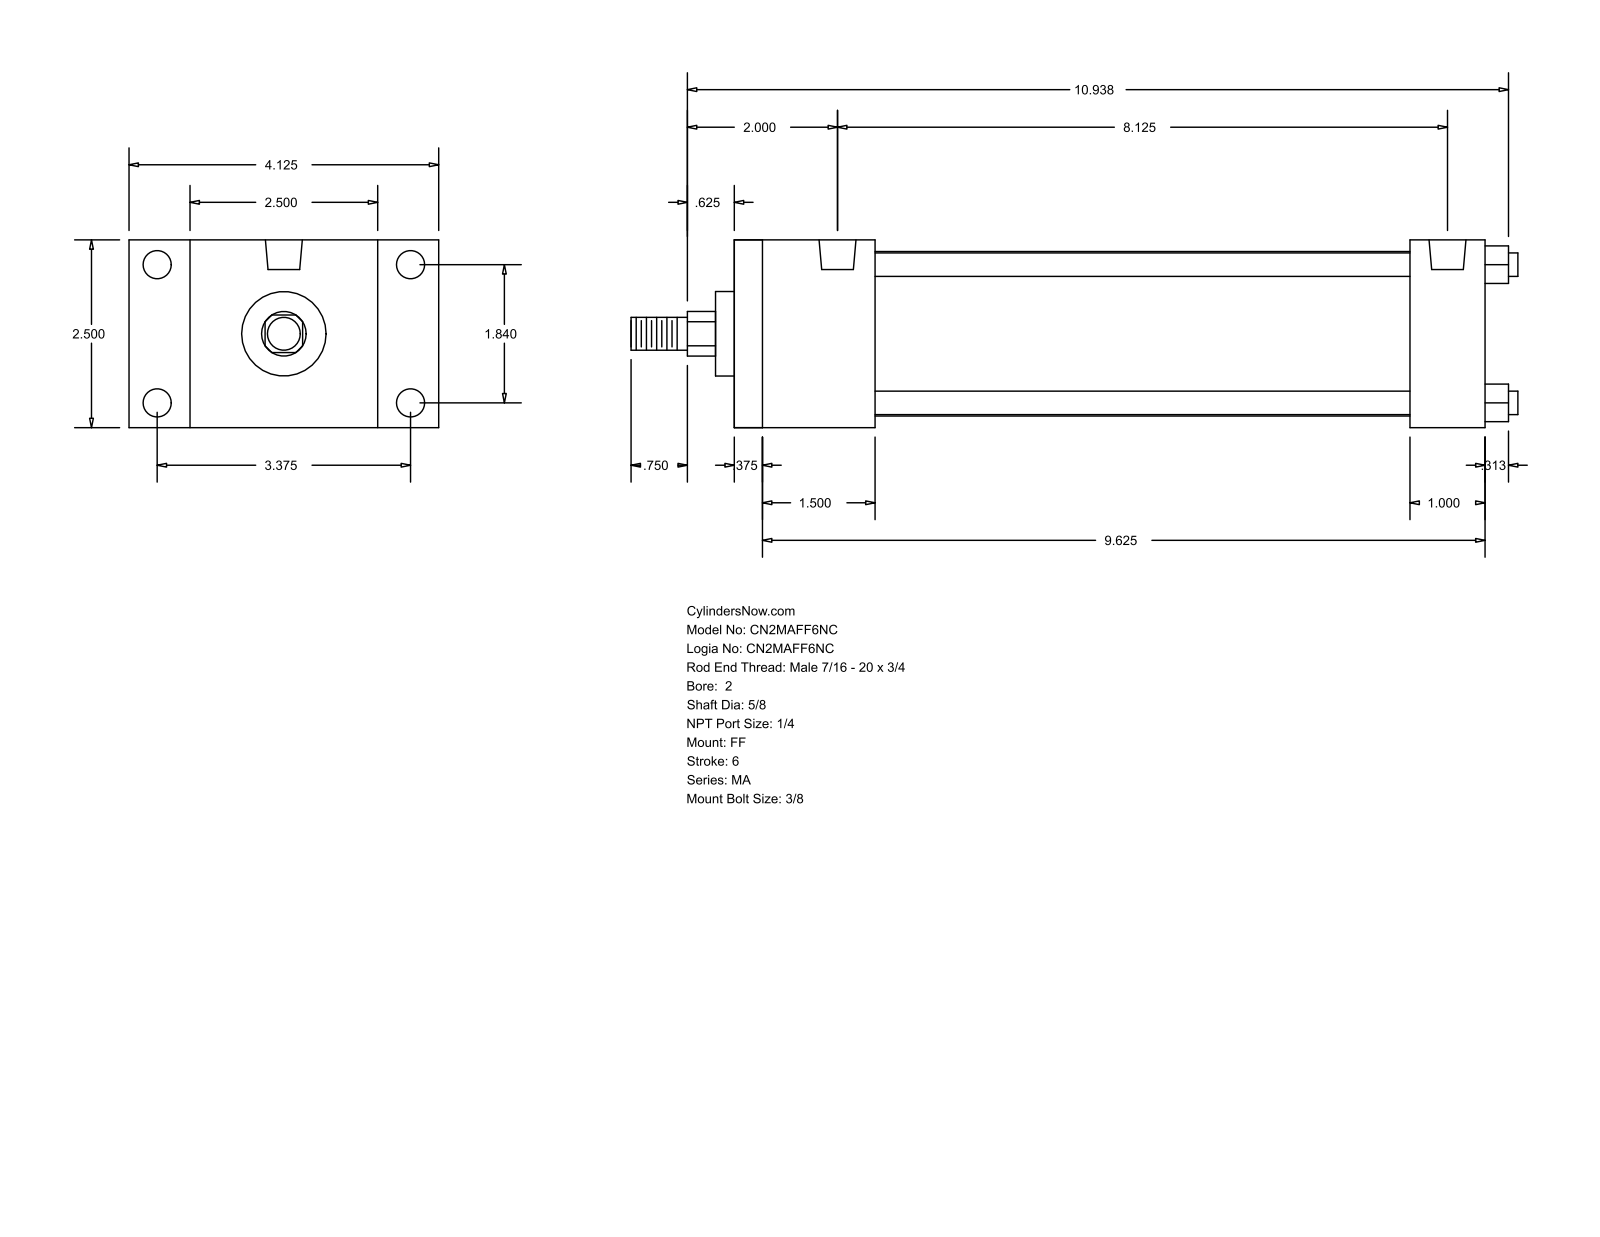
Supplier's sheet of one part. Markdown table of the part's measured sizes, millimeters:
| quantity | value |
| --- | --- |
| part name | MA_FF__0200_0.625 |
| STEP written by | GSSL Pune (CONFIG_CONTROL_DESIGN) |
| units | millimeters |
| bodies | 0 solids, 92 faces (64 planar, 28 cylindrical, 0 other) |
| overall size | 300.04 × 104.78 × 63.5 |
| round holes (diameter × count) | 7.94 × 4, 9.53 × 4, 12.49 × 2 |
| round bosses / shafts (diameter × count) | 7.94 × 4, 55.63 × 1, 28.57 × 1, 15.88 × 1, 11.11 × 1 |
| partial cylindrical surfaces (radius × count) | 7.54 × 1 |
| main face-to-face distances | 63.5, 254, 9.52, 244.48, 38.1, 47.62, 228.59, 219.07, 180.97, 206.38 |
| hole center spacings | 46.74, 85.72, 97.63, 206.38 |
